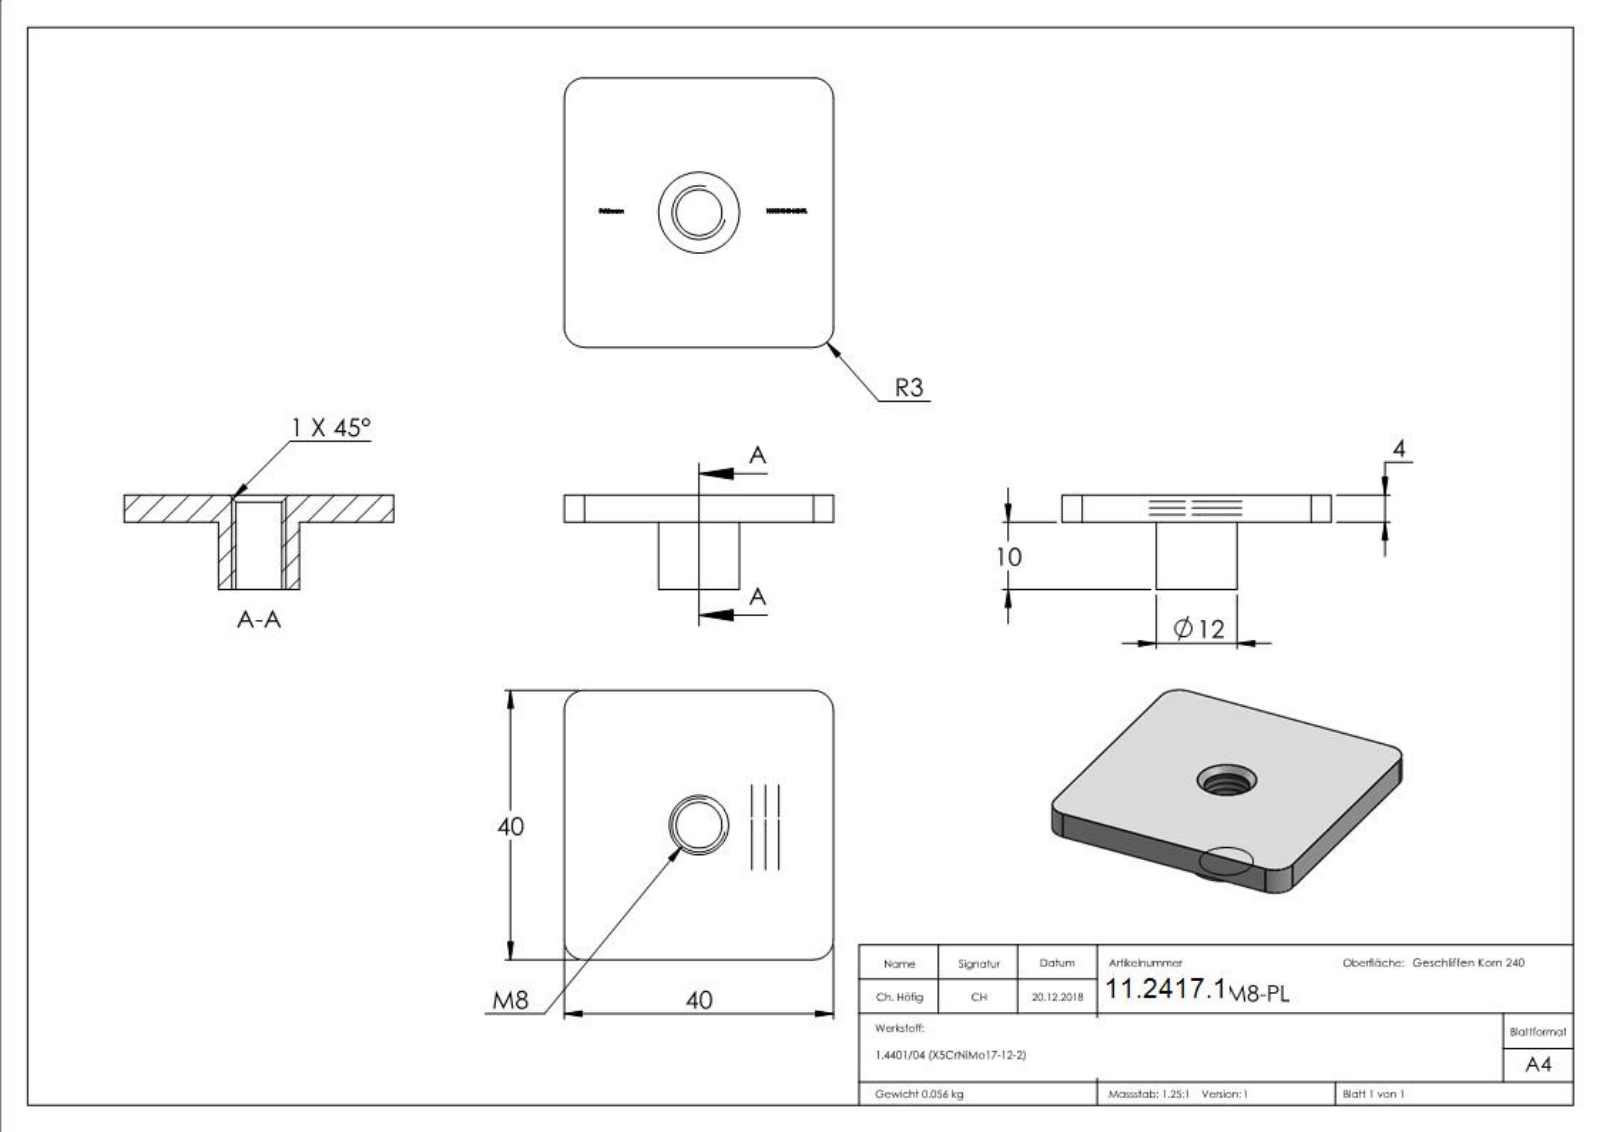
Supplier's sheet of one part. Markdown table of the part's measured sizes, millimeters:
| quantity | value |
| --- | --- |
| part name | 100034040-M8-PL |
| STEP written by | SolidWorks 2015 (CONFIG_CONTROL_DESIGN) |
| units | millimeters |
| bodies | 1 solid, 307 faces (167 planar, 8 cylindrical, 132 other) |
| overall size | 40 × 40 × 14 |
| volume | 6 980 mm³ |
| surface area | 4 401 mm² |
| round holes (diameter × count) | 6.8 × 1 |
| round bosses / shafts (diameter × count) | 12 × 1 |
| partial cylindrical surfaces (radius × count) | 3 × 4 |
| main face-to-face distances | 4, 40, 10, 14, 10.1, 3.9, 20, 20.18, 19.82, 24.09 |
